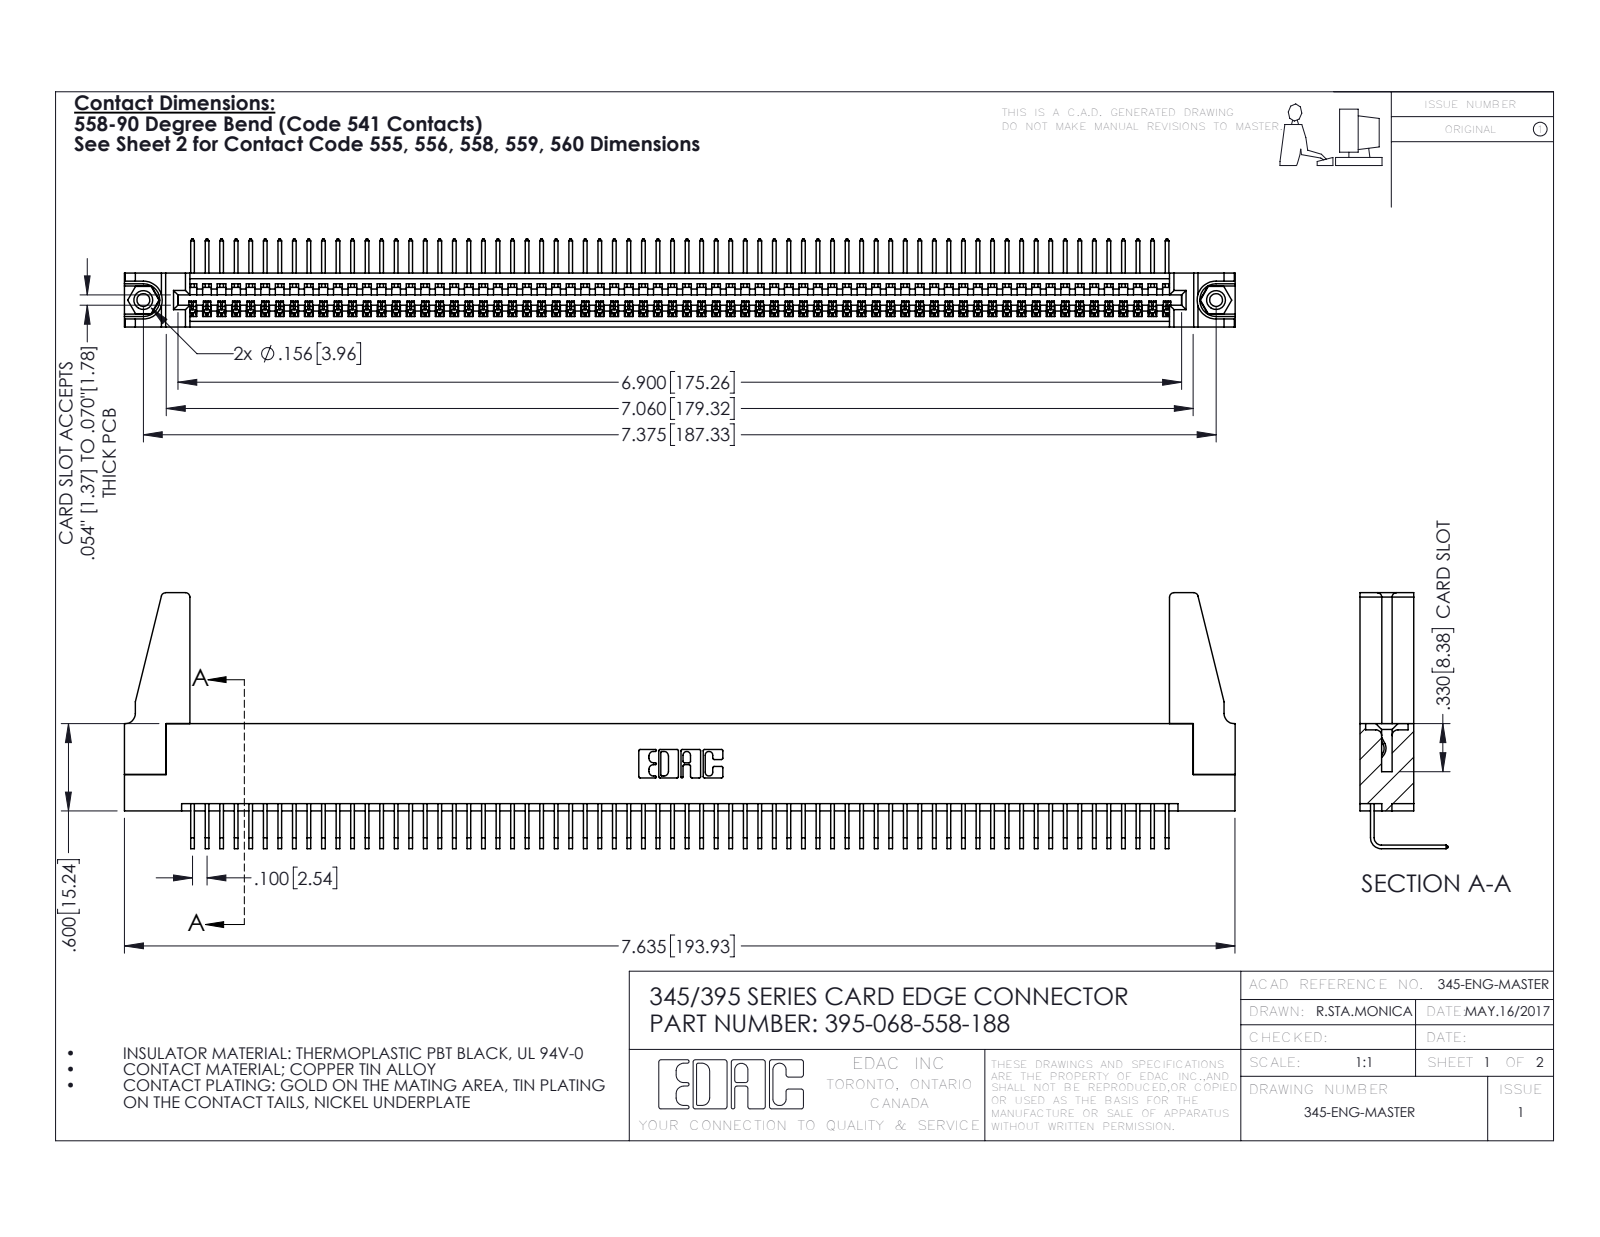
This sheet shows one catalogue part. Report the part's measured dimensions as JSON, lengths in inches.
{"part_name": "395-068-558-188; 345 Part_Flush Mounting Lugs - 0.156 Dia-TH; 345-250-001_345-250-001-102; 345-220-078_345-220-088 (+1 more)", "step_written_by": "SolidWorks 2016 (CONFIG_CONTROL_DESIGN)", "units": "inches", "bodies": {"solids": 73, "faces": 4330, "planar": 3008, "cylindrical": 1306, "other": 16}, "overall_size": [7.636, 1.759, 0.605], "volume_in3": 1.349, "surface_area_in2": 46.31, "round_holes": [[0.089, 2], [0.125, 2], [0.156, 2], [0.064, 1]], "round_bosses_or_shafts": [[0.155, 2]], "partial_cylinders_radius": [[0.006, 136], [0.01, 22], [0.03, 8], [0.007, 6], [0.031, 6], [0.026, 3], [0.031, 2], [0.04, 2]], "face_to_face_distances": [0.072, 0.298, 0.37, 0.2, 0.098, 0.272, 0.025, 0.225, 0.149, 0.072], "hole_center_spacings": [0.27, 7.139, 7.375]}
